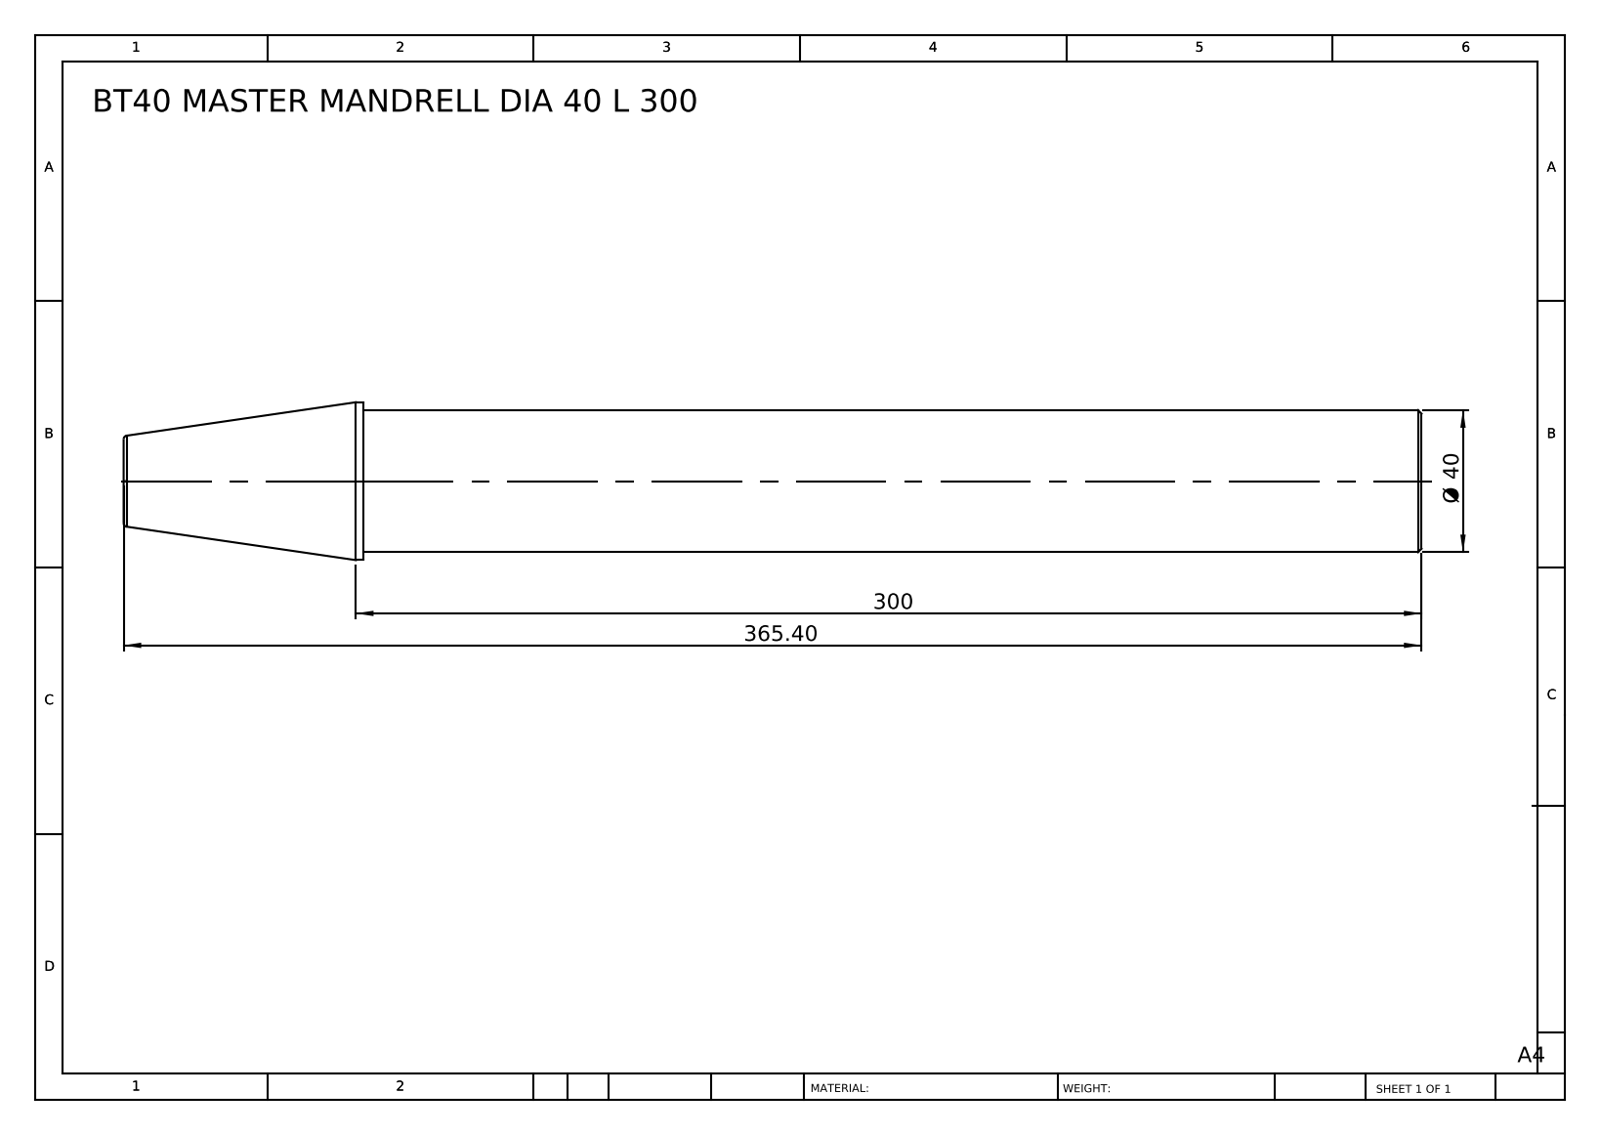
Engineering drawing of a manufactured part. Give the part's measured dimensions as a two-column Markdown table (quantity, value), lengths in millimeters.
| quantity | value |
| --- | --- |
| part name | BT40 MASTER MANDRELL DIA 40 L 300 |
| STEP written by | SolidWorks 2014 (CONFIG_CONTROL_DESIGN) |
| units | millimeters |
| bodies | 1 solid, 13 faces (3 planar, 4 cylindrical, 6 other) |
| overall size | 365.4 × 44.45 × 44.45 |
| volume | 441 676 mm³ |
| surface area | 46 934 mm² |
| round bosses / shafts (diameter × count) | 44.45 × 1, 40 × 1 |
| main face-to-face distances | 365.4, 298, 67.4 |
